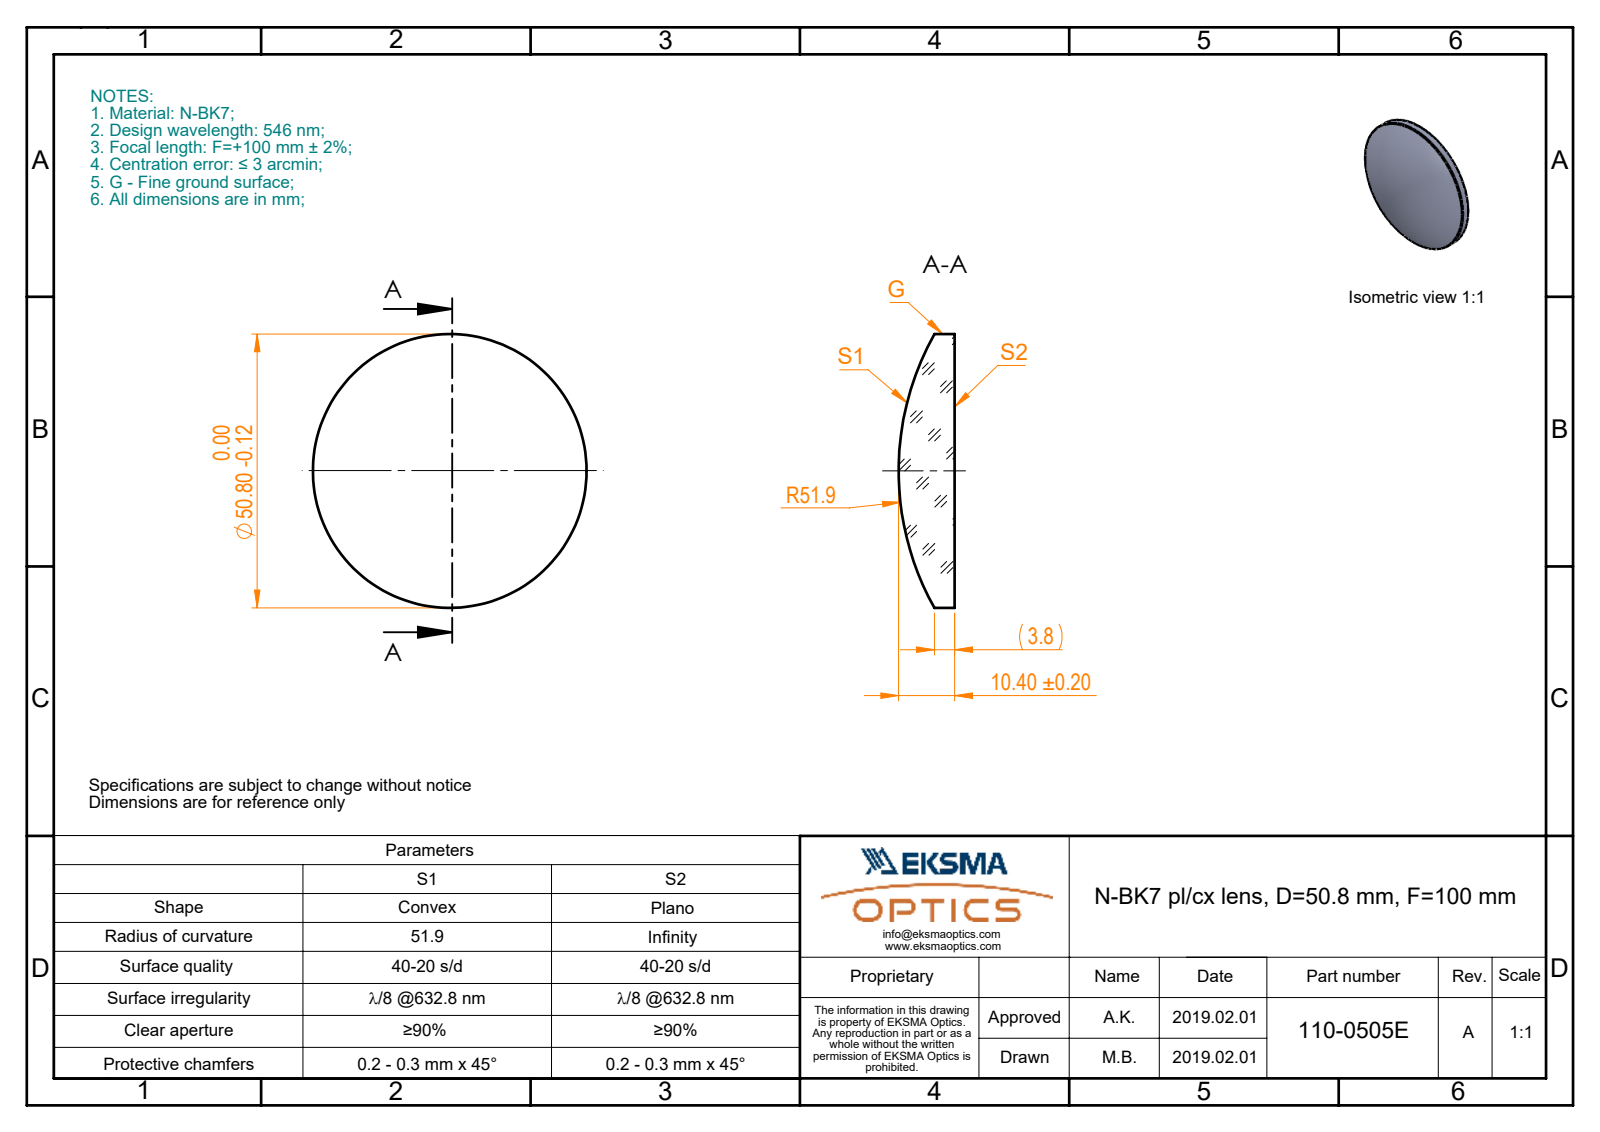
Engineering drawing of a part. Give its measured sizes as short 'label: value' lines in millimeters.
name: 110-0505E BK7 pl-cx 50.8 F100
written by: SolidWorks 2017 (CONFIG_CONTROL_DESIGN)
unit: mm
bodies: 1 solid, 5 faces (1 planar, 2 cylindrical, 2 other)
size: 50.8 × 50.8 × 10.4
volume: 14 499 mm³; area: 4 792 mm²
bosses: 1× ⌀50.8
